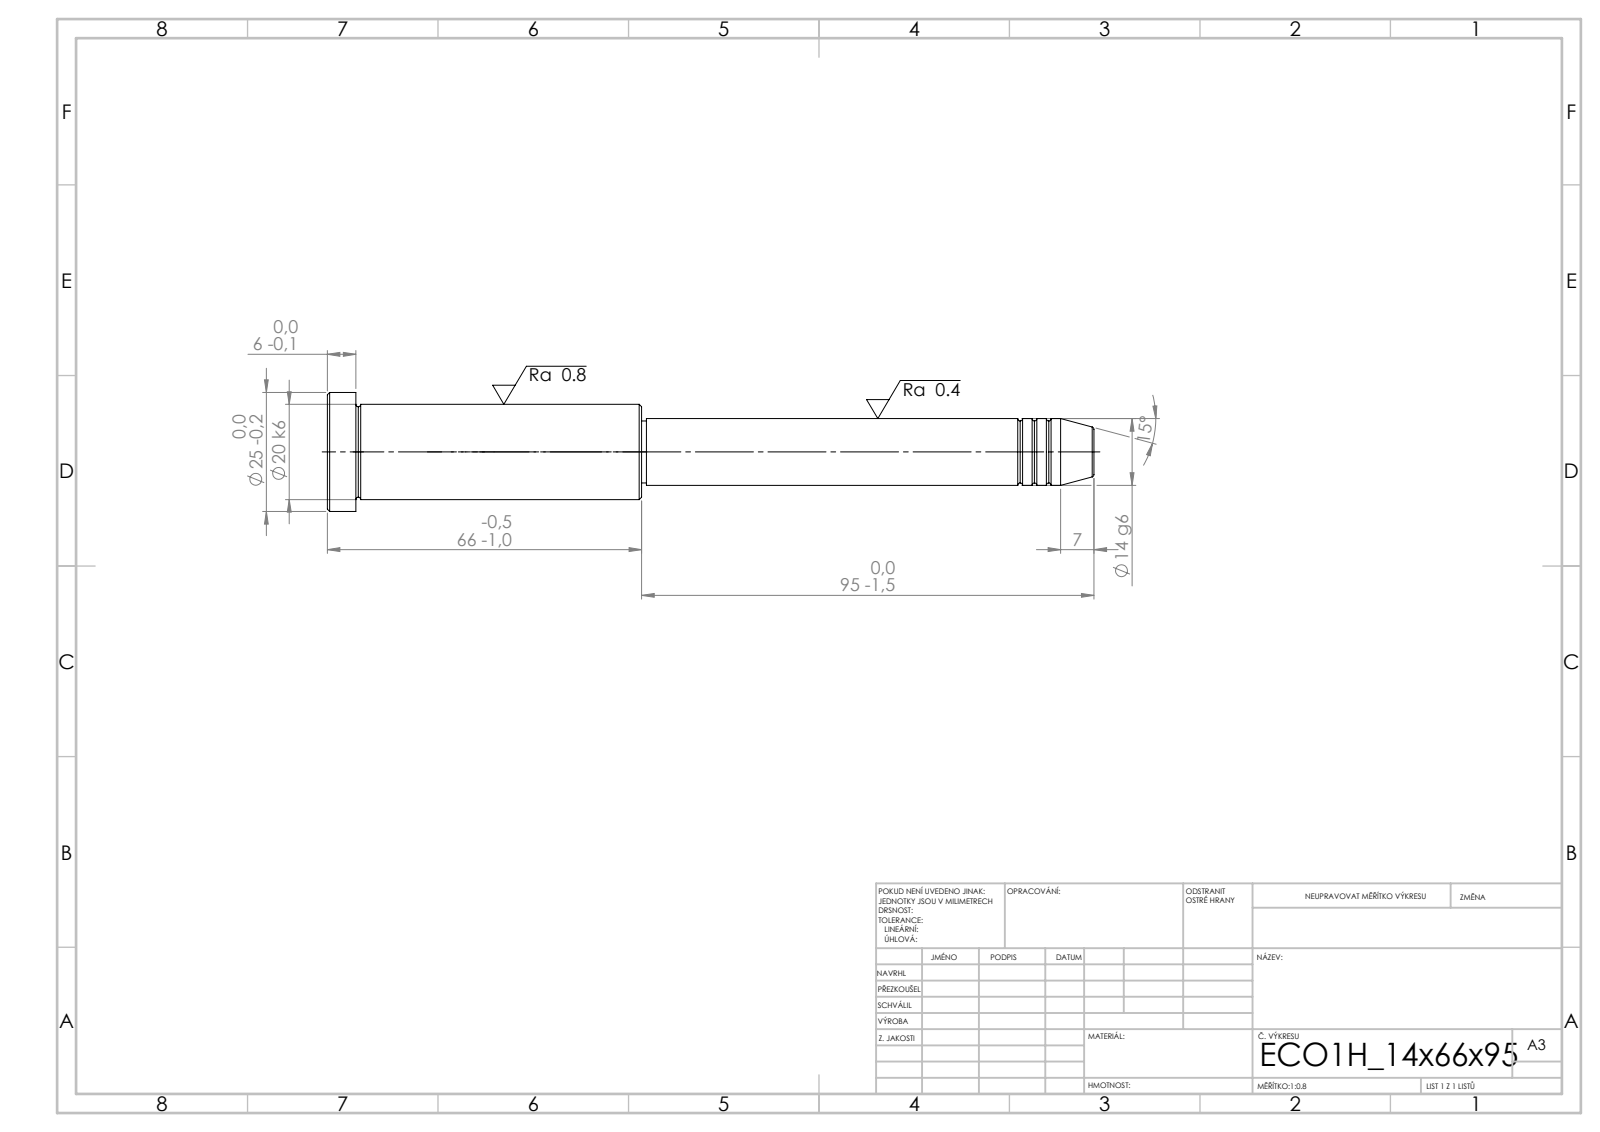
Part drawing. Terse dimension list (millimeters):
written by: SolidWorks 2019 (CONFIG_CONTROL_DESIGN)
unit: mm
bodies: 1 solid, 43 faces (5 planar, 14 cylindrical, 24 other)
size: 161 × 25 × 25
volume: 36 042 mm³; area: 9 390 mm²
bosses: 1× ⌀25, 1× ⌀20, 1× ⌀14, 1× ⌀13
face distances: 6, 60, 66, 95, 155, 161, 94, 1, 61, 67
